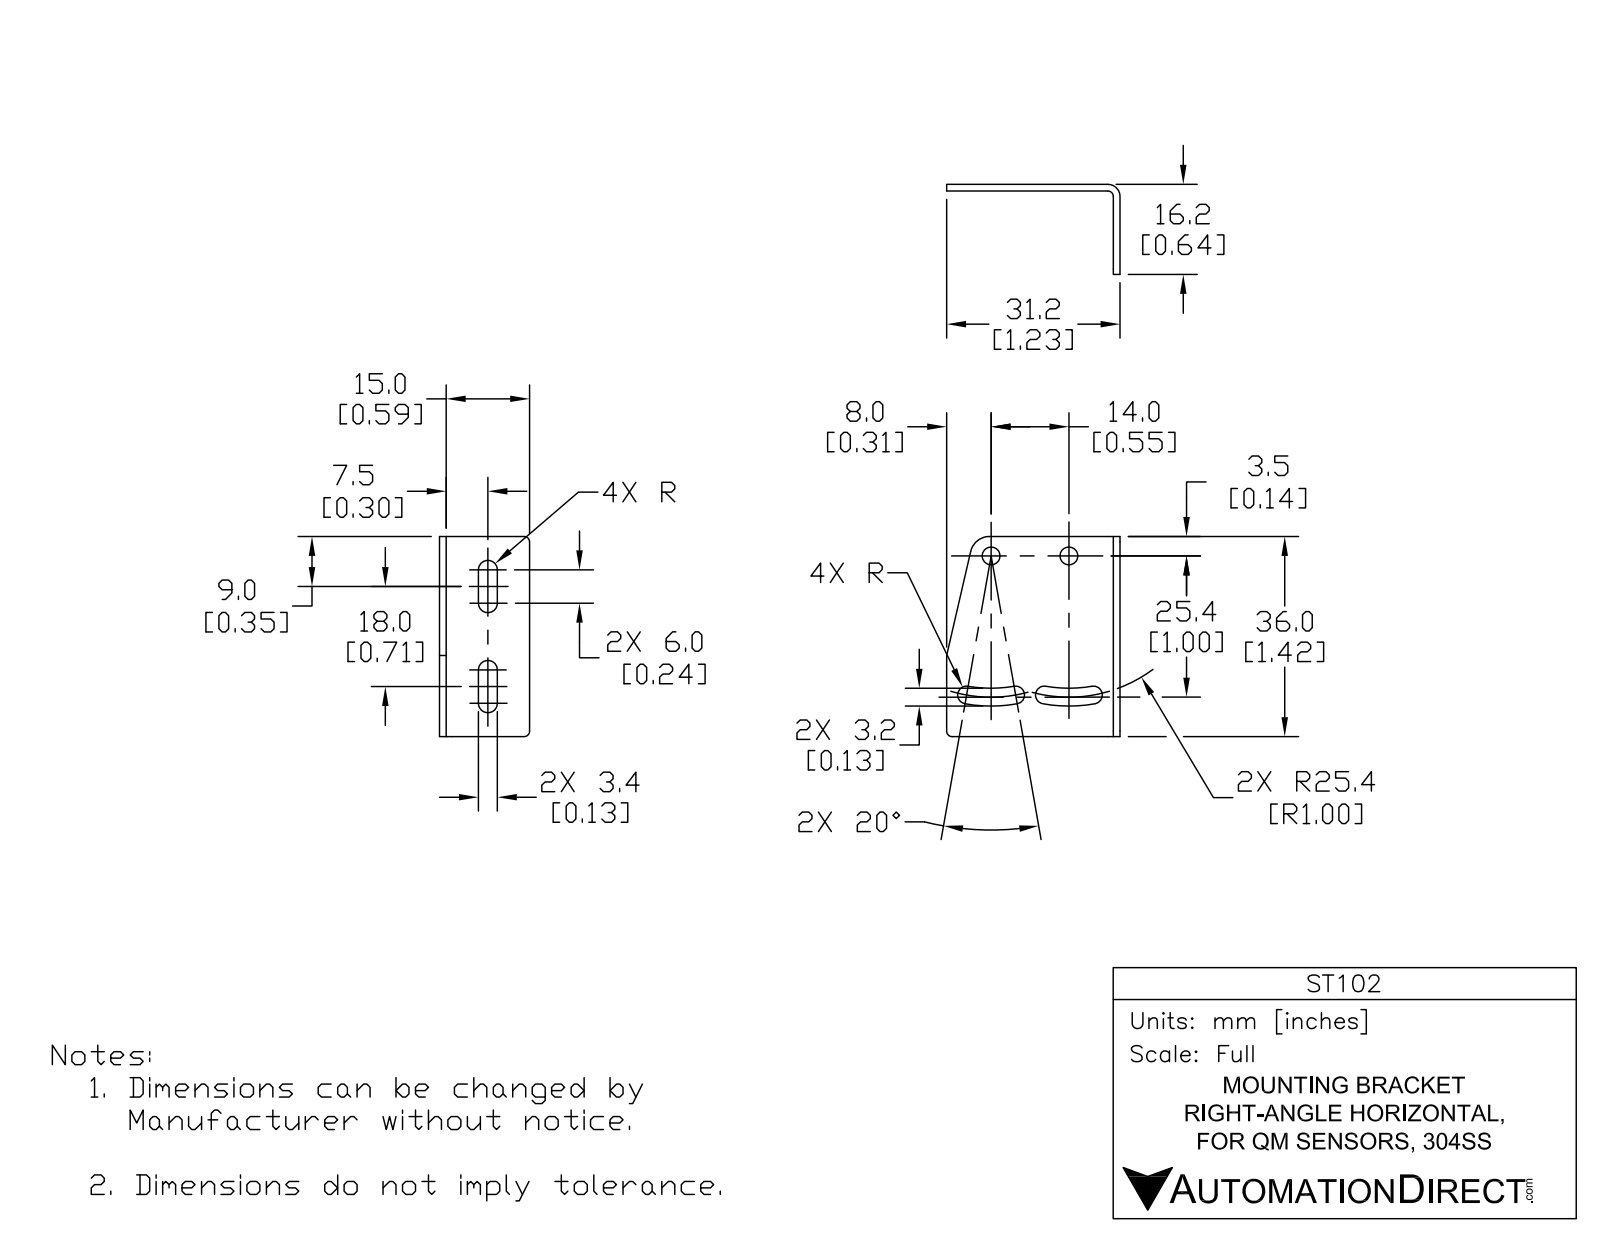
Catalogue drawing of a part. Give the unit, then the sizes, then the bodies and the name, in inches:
Units: inches
Overall size (bounding box): 1.417 × 1.228 × 0.638
Round holes (diameter × count): ⌀0.126 ×2
Partial cylindrical surfaces — rounded edges, fillets, slot ends (radius × count): R0.063 ×4, R0.067 ×4, R0.039 ×3, R0.937 ×2, R1.063 ×2, R0.079 ×1, R0.126 ×1, R0.138 ×1
Main face-to-face distances: 0.047, 1.417, 0.591, 0.638, 0.228, 0.362, 1.181, 1.228, 0.276, 0.134
Hole centre spacings: 0.551
Volume: 0.104 in³ · Surface area: 4.906 in²
Bodies: 1 solid, 37 faces (13 planar, 24 cylindrical, 0 other)
Part name (STEP PRODUCT): ST102
STEP written by: SolidWorks 2017 (AUTOMOTIVE_DESIGN)
